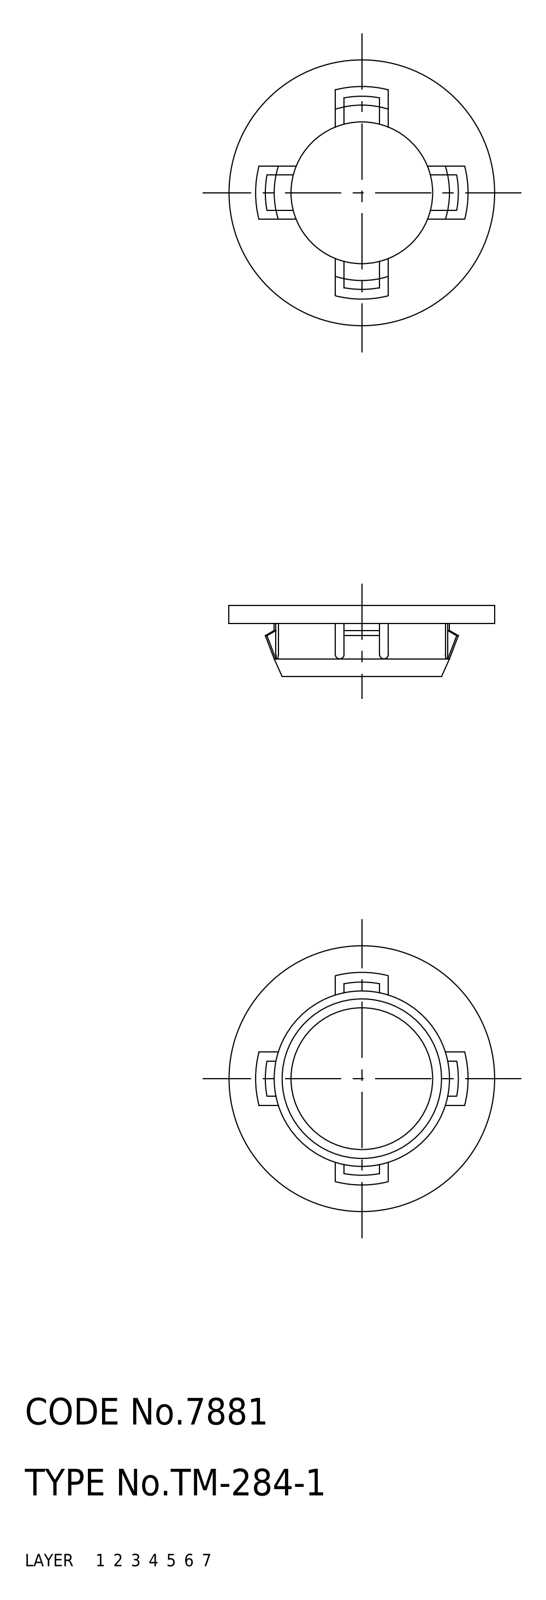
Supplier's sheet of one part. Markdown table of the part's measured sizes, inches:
| quantity | value |
| --- | --- |
| part name | grommet |
| STEP written by | CADfix (AUTOMOTIVE_DESIGN) |
| units | inches |
| bodies | 1 solid, 57 faces (0 planar, 0 cylindrical, 57 other) |
| overall size | 1.181 × 1.181 × 0.315 |
| volume | 0.087 in³ |
| surface area | 3.205 in² |
